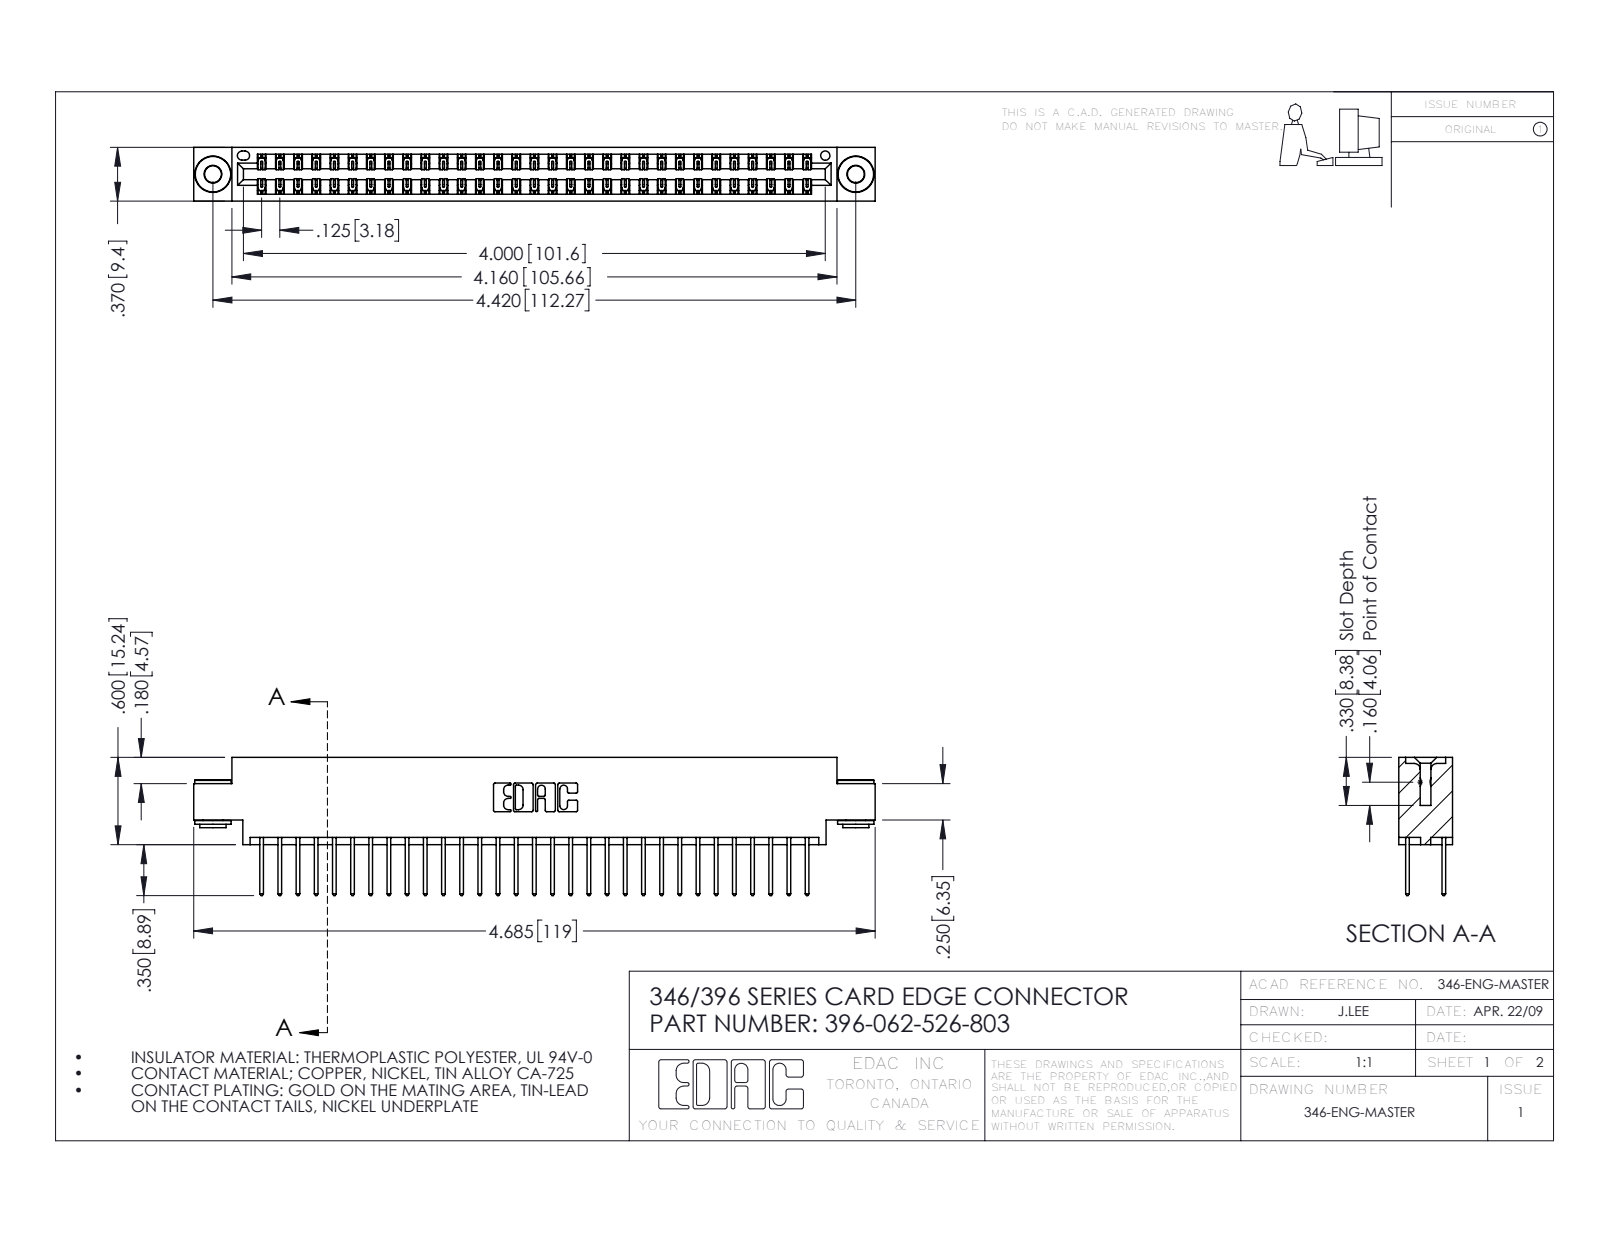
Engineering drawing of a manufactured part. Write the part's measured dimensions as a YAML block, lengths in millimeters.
part_name: "345-292-001_345-293-126; 345-250-002_345-250-002-102; 396-062-526-803; 346 Part_0.170 Offset - 0.156 Dia-TH"
step_written_by: "SolidWorks 2016 (CONFIG_CONTROL_DESIGN)"
units: millimeters
bodies: {solids: 65, faces: 3388, planar: 2260, cylindrical: 1120, other: 8}
overall_size: [119, 24.1, 9.4]
volume: 11500
surface_area: 16460
round_holes:
  - {diameter: 2.9, count: 2}
  - {diameter: 4, count: 2}
  - {diameter: 1.6, count: 1}
round_bosses_or_shafts:
  - {diameter: 6.4, count: 2}
  - {diameter: 4.6, count: 2}
  - {diameter: 3.5, count: 2}
partial_cylinders:
  - {radius: 0.2, count: 93}
  - {radius: 0.3, count: 62}
  - {radius: 0.3, count: 22}
  - {radius: 0.2, count: 6}
  - {radius: 0.8, count: 6}
  - {radius: 0.7, count: 3}
  - {radius: 0.4, count: 2}
  - {radius: 0.6, count: 2}
face_to_face_distances: [1.2, 8.2, 6.4, 9.4, 0.6, 1.8, 7.6, 7, 3.8, 5.6]
hole_center_spacings: [6.2, 107, 112.3]
